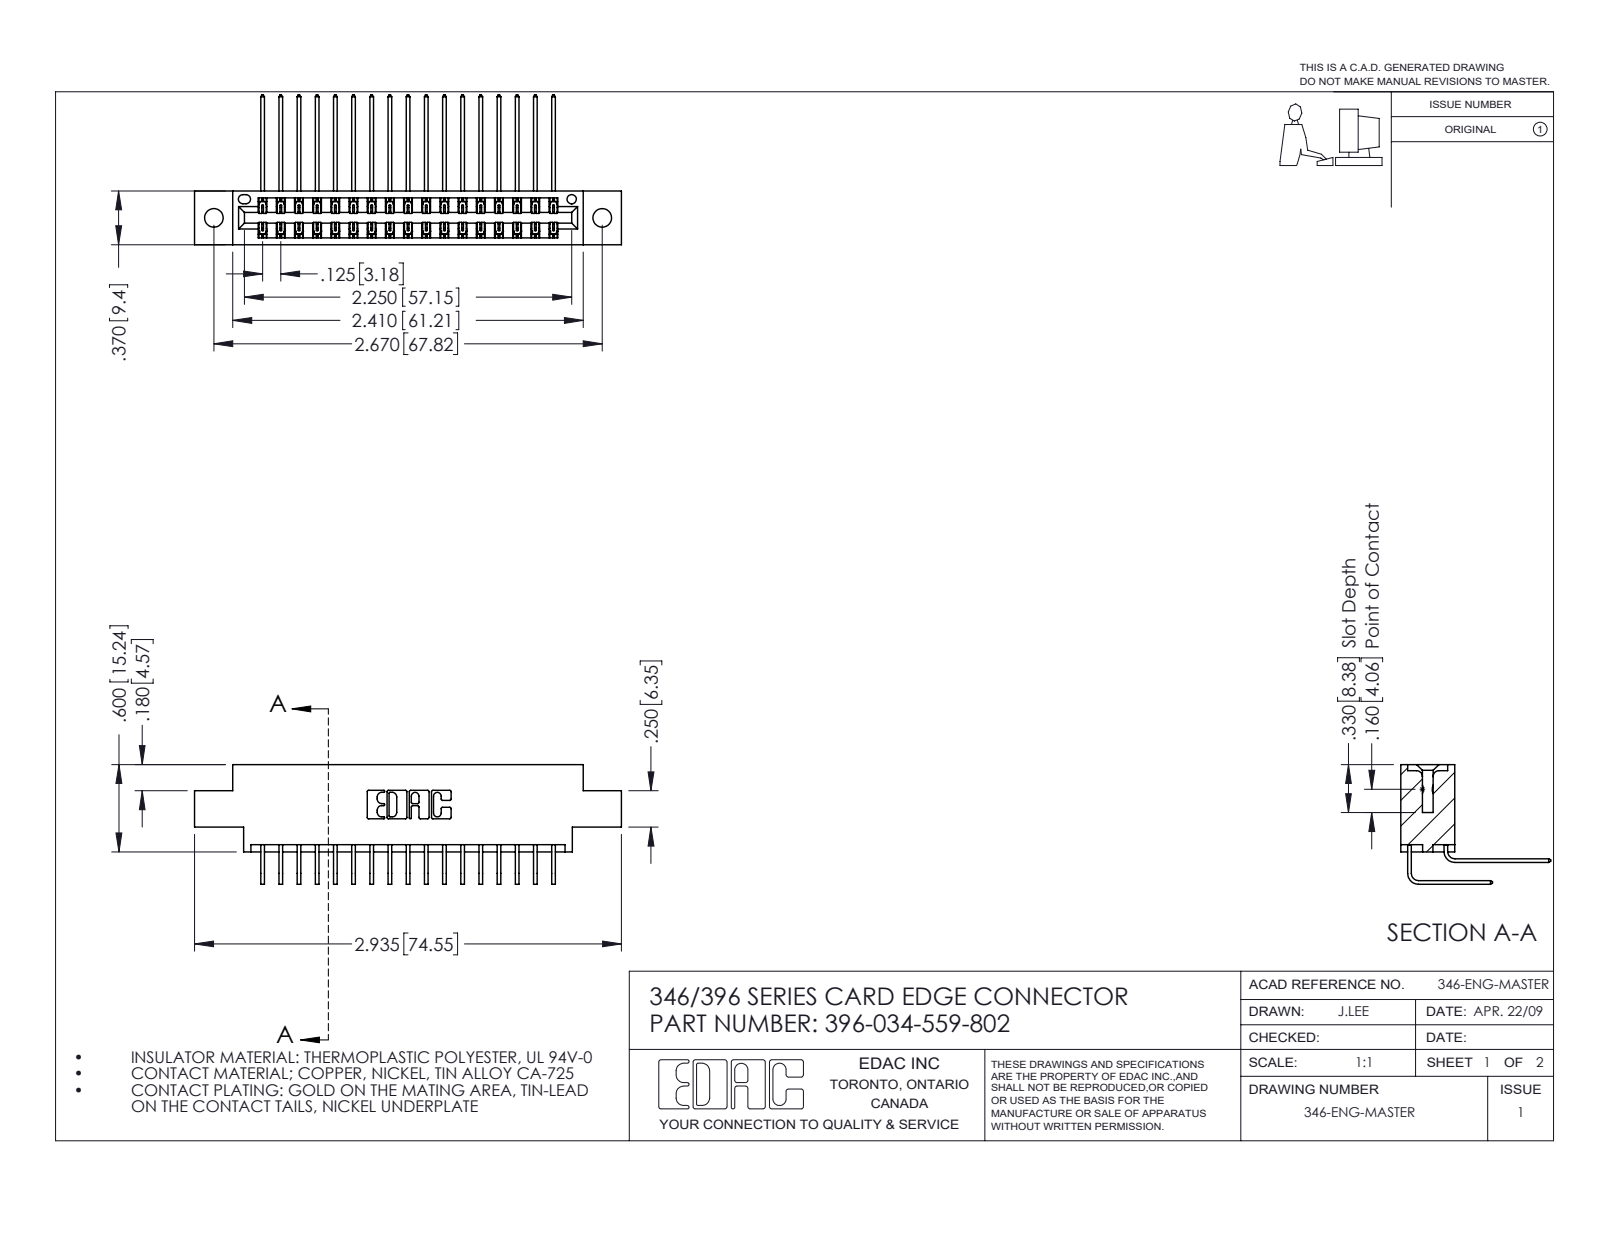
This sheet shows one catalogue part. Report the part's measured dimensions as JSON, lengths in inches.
{"part_name": "396-034-559-802; 345-292-001_559 Tail - 2; 346 Part_0.170 Offset - 0.128 Dia; 345-292-001_558 559 Tail - 1", "step_written_by": "SolidWorks 2016 (CONFIG_CONTROL_DESIGN)", "units": "inches", "bodies": {"solids": 35, "faces": 1962, "planar": 1338, "cylindrical": 624, "other": 0}, "overall_size": [2.935, 1.03, 0.823], "volume_in3": 0.432, "surface_area_in2": 15.8, "round_holes": [[0.128, 2], [0.064, 1]], "partial_cylinders_radius": [[0.006, 51], [0.01, 22], [0.007, 6], [0.031, 6], [0.026, 3], [0.014, 2], [0.022, 2], [0.024, 2]], "face_to_face_distances": [0.048, 0.322, 0.37, 0.25, 0.025, 0.072, 0.298, 0.275, 0.15, 0.148], "hole_center_spacings": [0.246, 2.463, 2.67]}
